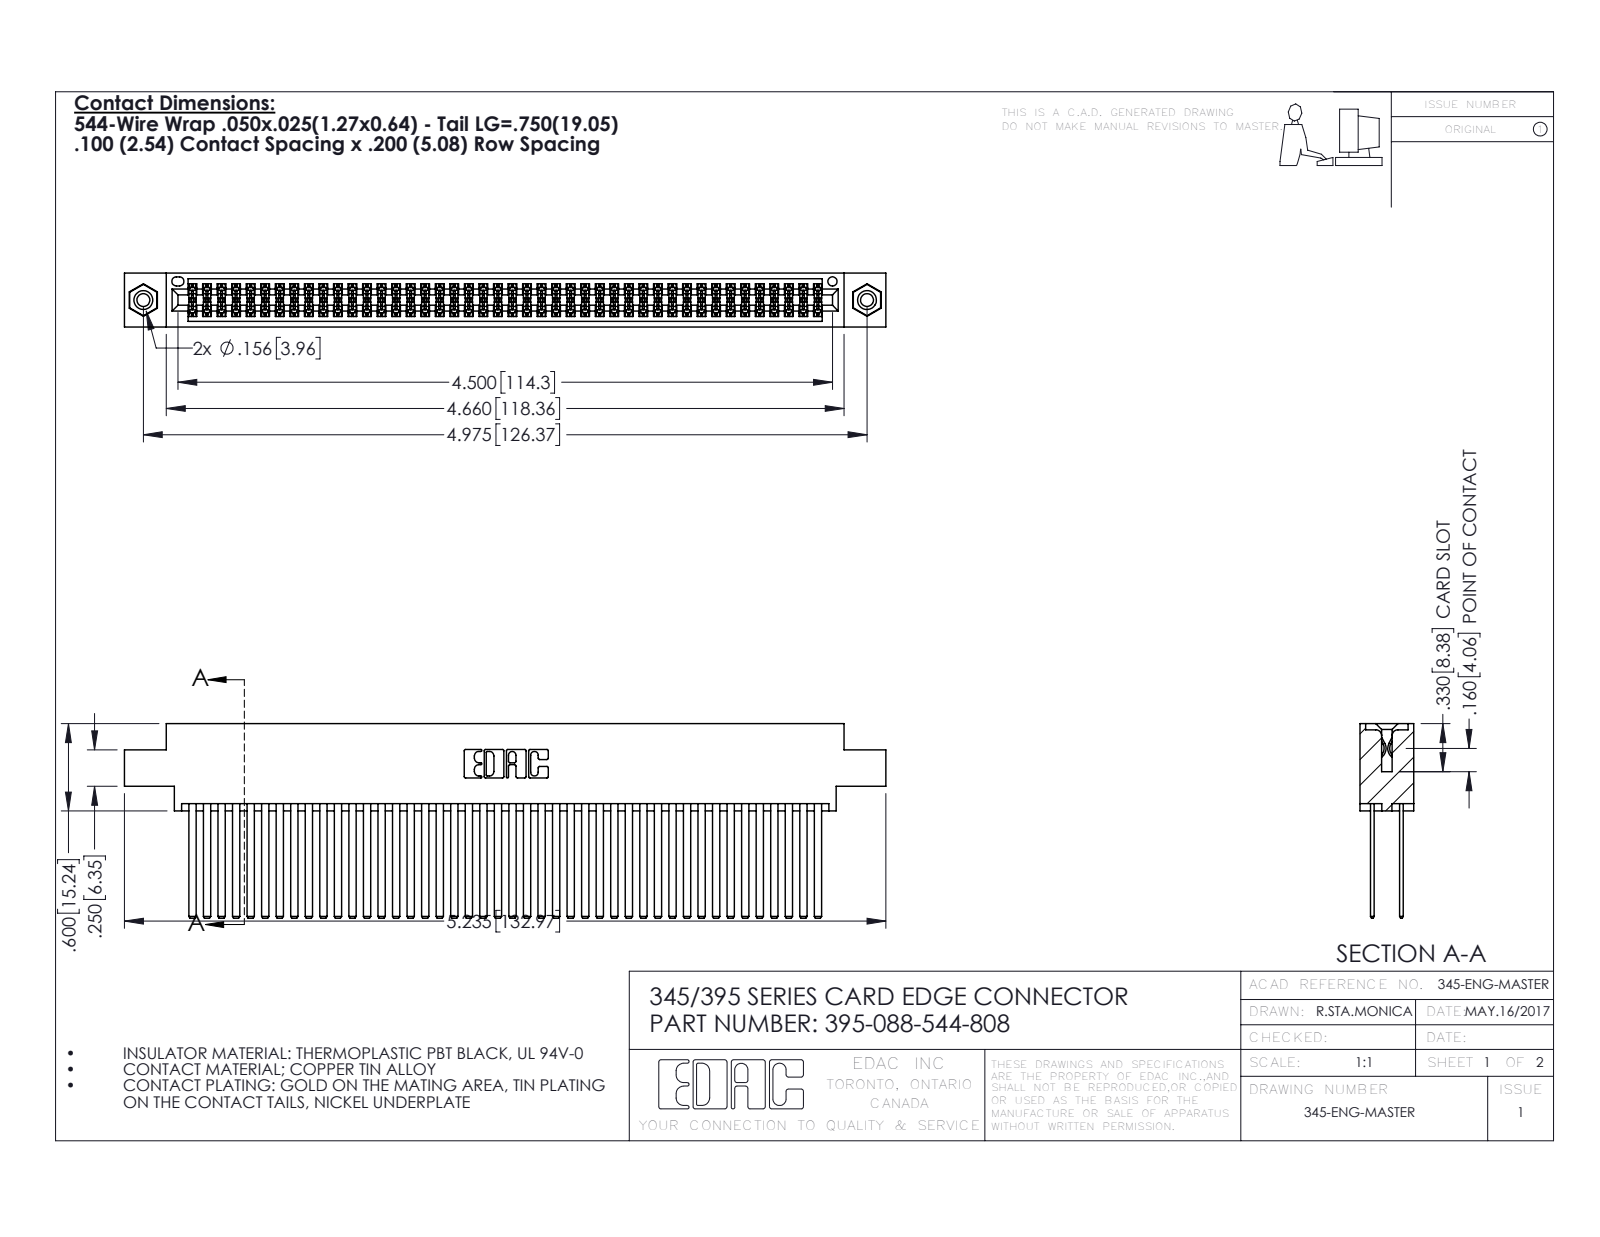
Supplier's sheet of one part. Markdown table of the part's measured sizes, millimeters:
| quantity | value |
| --- | --- |
| part name | 345-250-001_345-250-003-102; 345-292-001_345-293-144; 345 Part_0.170 Offset - 0.156 Dia-TI; 395-088-544-808 |
| STEP written by | SolidWorks 2016 (CONFIG_CONTROL_DESIGN) |
| units | millimeters |
| bodies | 91 solids, 4062 faces (2668 planar, 1378 cylindrical, 16 other) |
| overall size | 133 × 34 × 9.4 |
| volume | 14 000 mm³ |
| surface area | 24 580 mm² |
| round holes (diameter × count) | 2.3 × 2, 3.2 × 2, 4 × 2, 1.6 × 1 |
| round bosses / shafts (diameter × count) | 3.9 × 2 |
| partial cylindrical surfaces (radius × count) | 0.2 × 132, 0.3 × 22, 0.2 × 6, 0.8 × 6, 0.7 × 3, 0.4 × 2, 0.5 × 2, 0.6 × 2 |
| main face-to-face distances | 5.1, 0.6, 1.8, 2.5, 6.9, 7.6, 5.7, 4.4, 9.4, 3.8 |
| hole center spacings | 6.9, 120.4, 126.4 |
